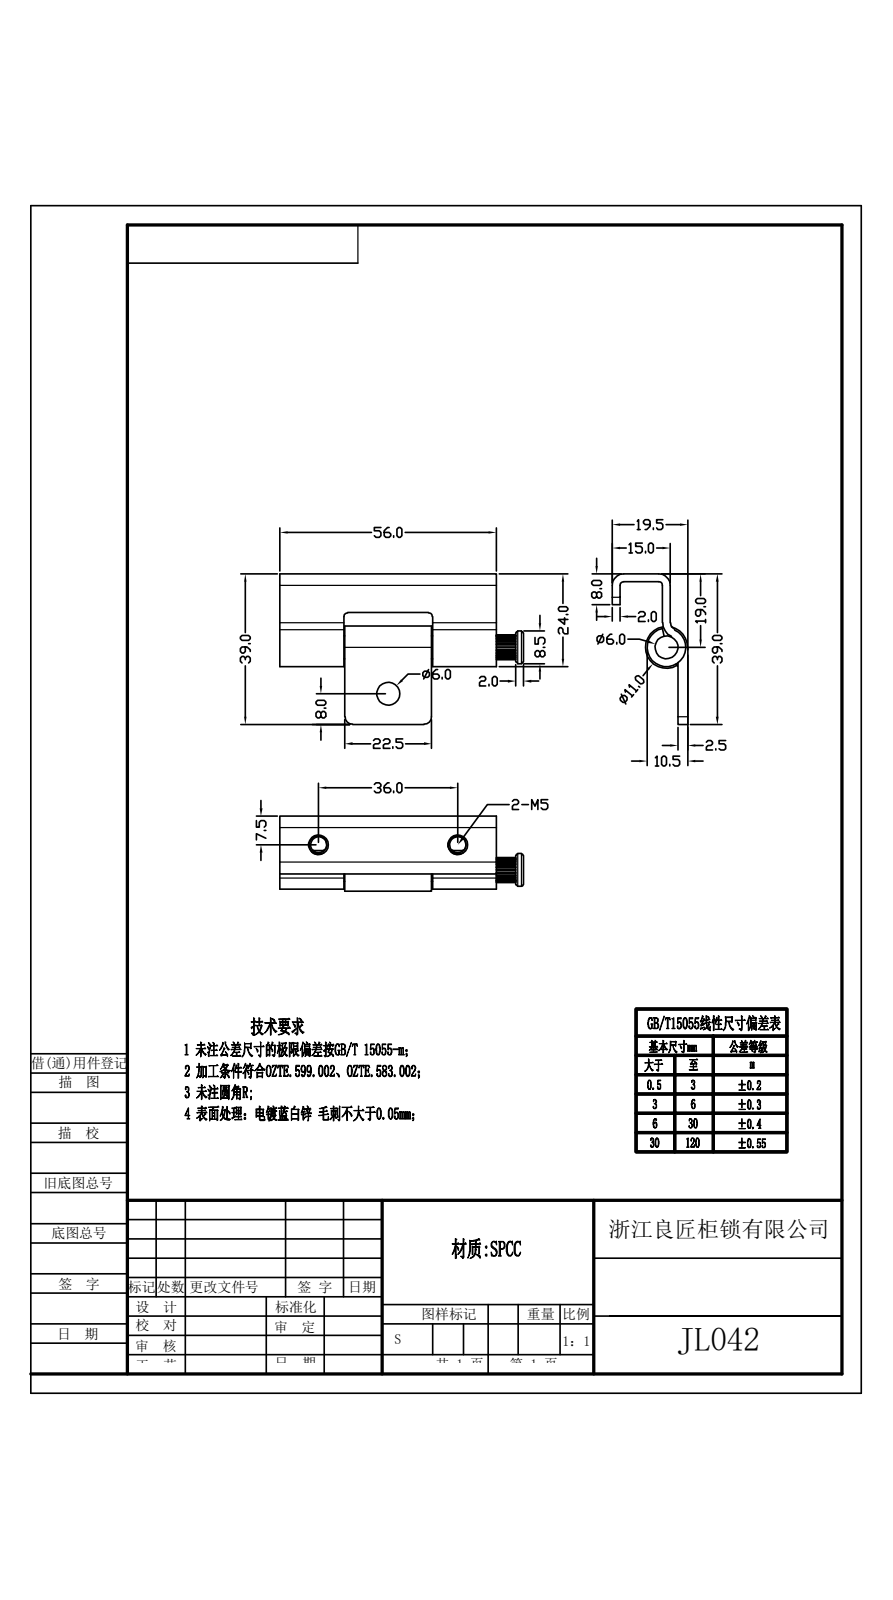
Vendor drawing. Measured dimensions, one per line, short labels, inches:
written by: Rhino 8.5 (CONFIG_CONTROL_DESIGN)
unit: in
bodies: 3 solids, 128 faces (25 planar, 87 cylindrical, 16 other)
size: 2.48 × 1.535 × 0.768
volume: 0.551 in³; area: 14 in²
holes: 2× ⌀0.236
bosses: 1× ⌀0.433, 1× ⌀0.394, 1× ⌀0.335
rounds: 30× R0.004, 5× R0.079, 4× R0.039, 2× R0.118, 1× R0.127, 1× R0.157
face distances: 0.079, 0.512, 0.591, 0.256, 0.177, 0.157, 0.098, 0.669, 0.768, 0.433
